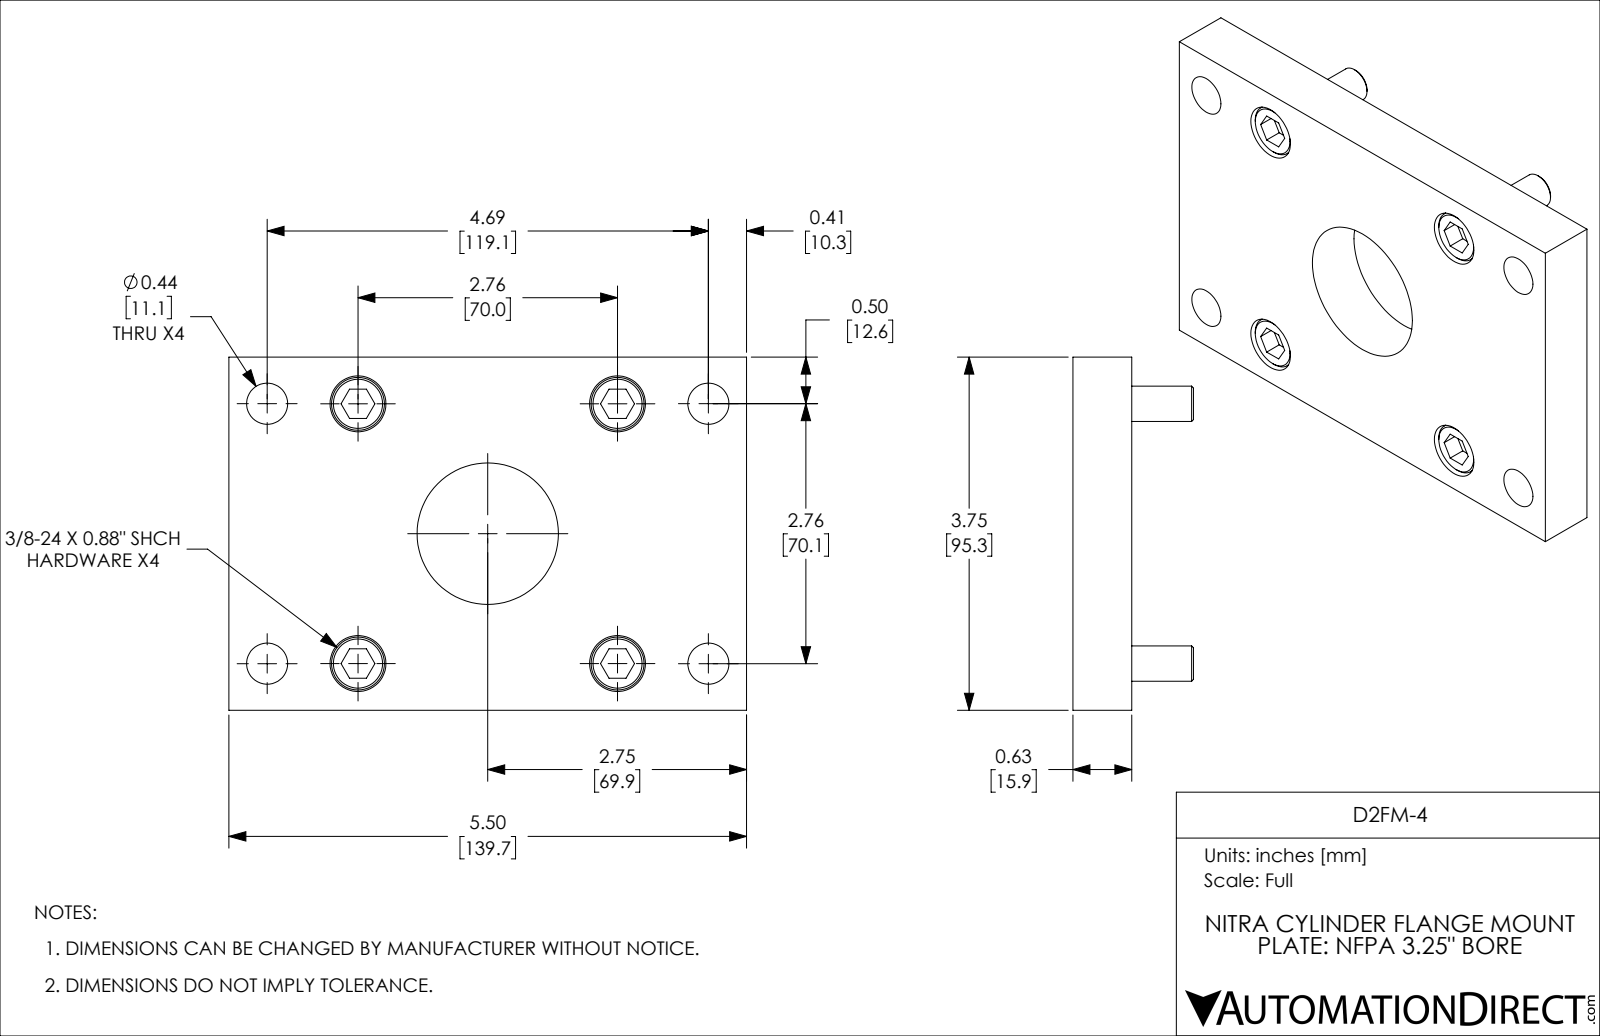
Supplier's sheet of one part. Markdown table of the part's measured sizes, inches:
| quantity | value |
| --- | --- |
| part name | D2FM-4 |
| STEP written by | SolidWorks 2019 (CONFIG_CONTROL_DESIGN) |
| units | inches |
| bodies | 5 solids, 108 faces (50 planar, 42 cylindrical, 16 other) |
| overall size | 5.5 × 3.75 × 1.281 |
| volume | 11.54 in³ |
| surface area | 66.99 in² |
| round holes (diameter × count) | 0.406 × 4, 0.437 × 4, 0.594 × 4, 1.502 × 1 |
| round bosses / shafts (diameter × count) | 0.562 × 4, 0.375 × 2, 0.375 × 2 |
| main face-to-face distances | 0.625, 3.75, 5.5, 0.219, 0.406, 0.594, 0.375, 0.031, 0.656, 0.875 |
| hole center spacings | 0.965, 1.95, 2.72, 2.757, 2.923, 3.723, 4.633, 2.76 |
